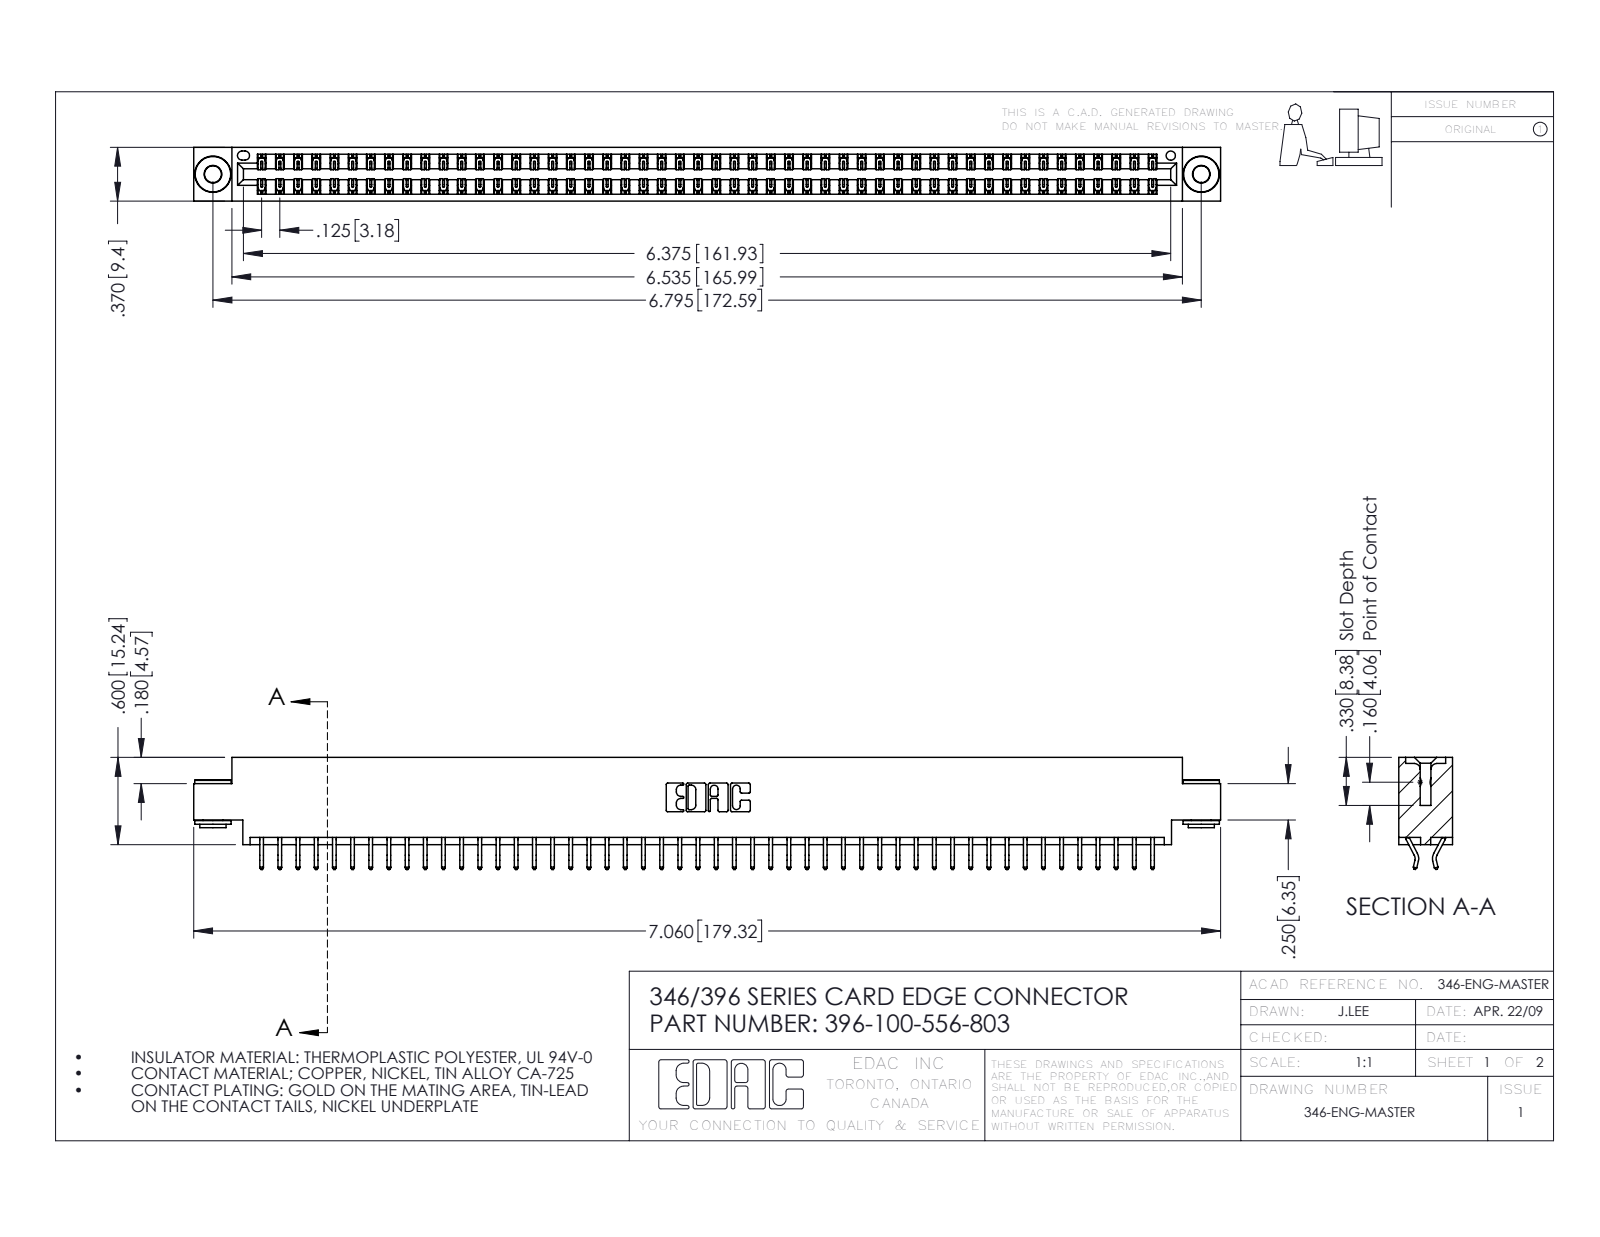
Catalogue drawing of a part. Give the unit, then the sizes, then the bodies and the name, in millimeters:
Units: millimetres
Overall size (bounding box): 179.3 × 19.6 × 9.4
Round holes (diameter × count): ⌀2.9 ×2, ⌀4 ×2, ⌀1.6 ×1
Round bosses / shafts (diameter × count): ⌀6.4 ×2, ⌀4.6 ×2, ⌀3.5 ×2
Partial cylindrical surfaces — rounded edges, fillets, slot ends (radius × count): R0.2 ×150, R0.3 ×22, R0.2 ×6, R0.8 ×6, R0.7 ×3, R0.3 ×2, R0.4 ×2, R0.6 ×2
Main face-to-face distances: 1.2, 8.2, 9.4, 6.4, 0.6, 7, 1.8, 7.6, 3.8, 5.6
Hole centre spacings: 6.2, 167.3, 172.6
Volume: 17 400 mm³ · Surface area: 24 350 mm²
Bodies: 103 solids, 5964 faces (3990 planar, 1966 cylindrical, 8 other)
Part name (STEP PRODUCT): 346 Part_0.170 Offset - 0.156 Dia-TH; 345-250-002_345-250-002-102; 396-100-556-803; 345-292-001_556 Tail
STEP written by: SolidWorks 2016 (CONFIG_CONTROL_DESIGN)
